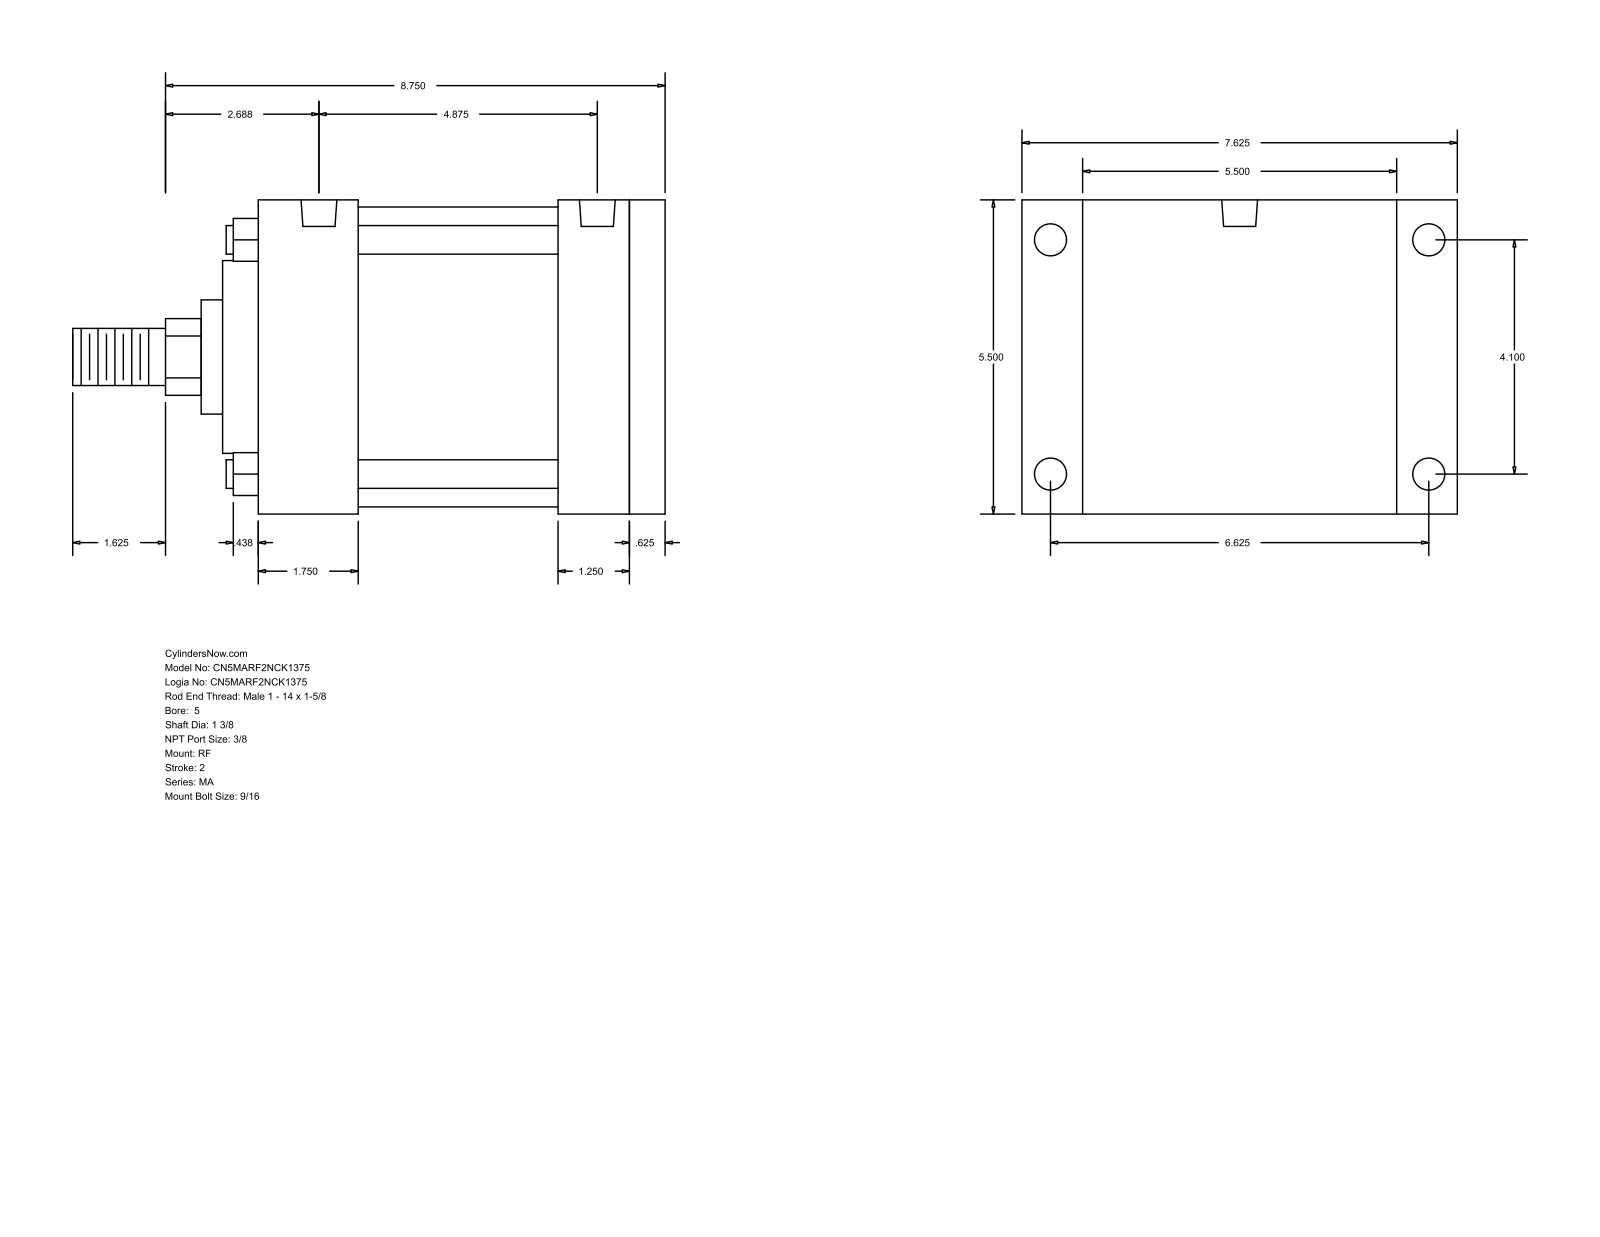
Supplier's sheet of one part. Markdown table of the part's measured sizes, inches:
| quantity | value |
| --- | --- |
| part name | MA_RF__0500_1.375 |
| STEP written by | GSSL Pune (CONFIG_CONTROL_DESIGN) |
| units | inches |
| bodies | 0 solids, 94 faces (65 planar, 29 cylindrical, 0 other) |
| overall size | 10.375 × 7.625 × 5.5 |
| round holes (diameter × count) | 0.437 × 4, 0.563 × 4, 0.627 × 2 |
| round bosses / shafts (diameter × count) | 0.5 × 4, 5.25 × 1, 3.375 × 1, 2 × 1, 1.375 × 1, 1 × 1 |
| partial cylindrical surfaces (radius × count) | 0.672 × 1 |
| main face-to-face distances | 5.5, 7.125, 0.625, 6.5, 1.75, 4.75, 5.375, 5.25, 3.5, 1.25 |
| hole center spacings | 0.188, 4.1, 4.5, 4.687, 6.625, 7.791, 4.875 |
